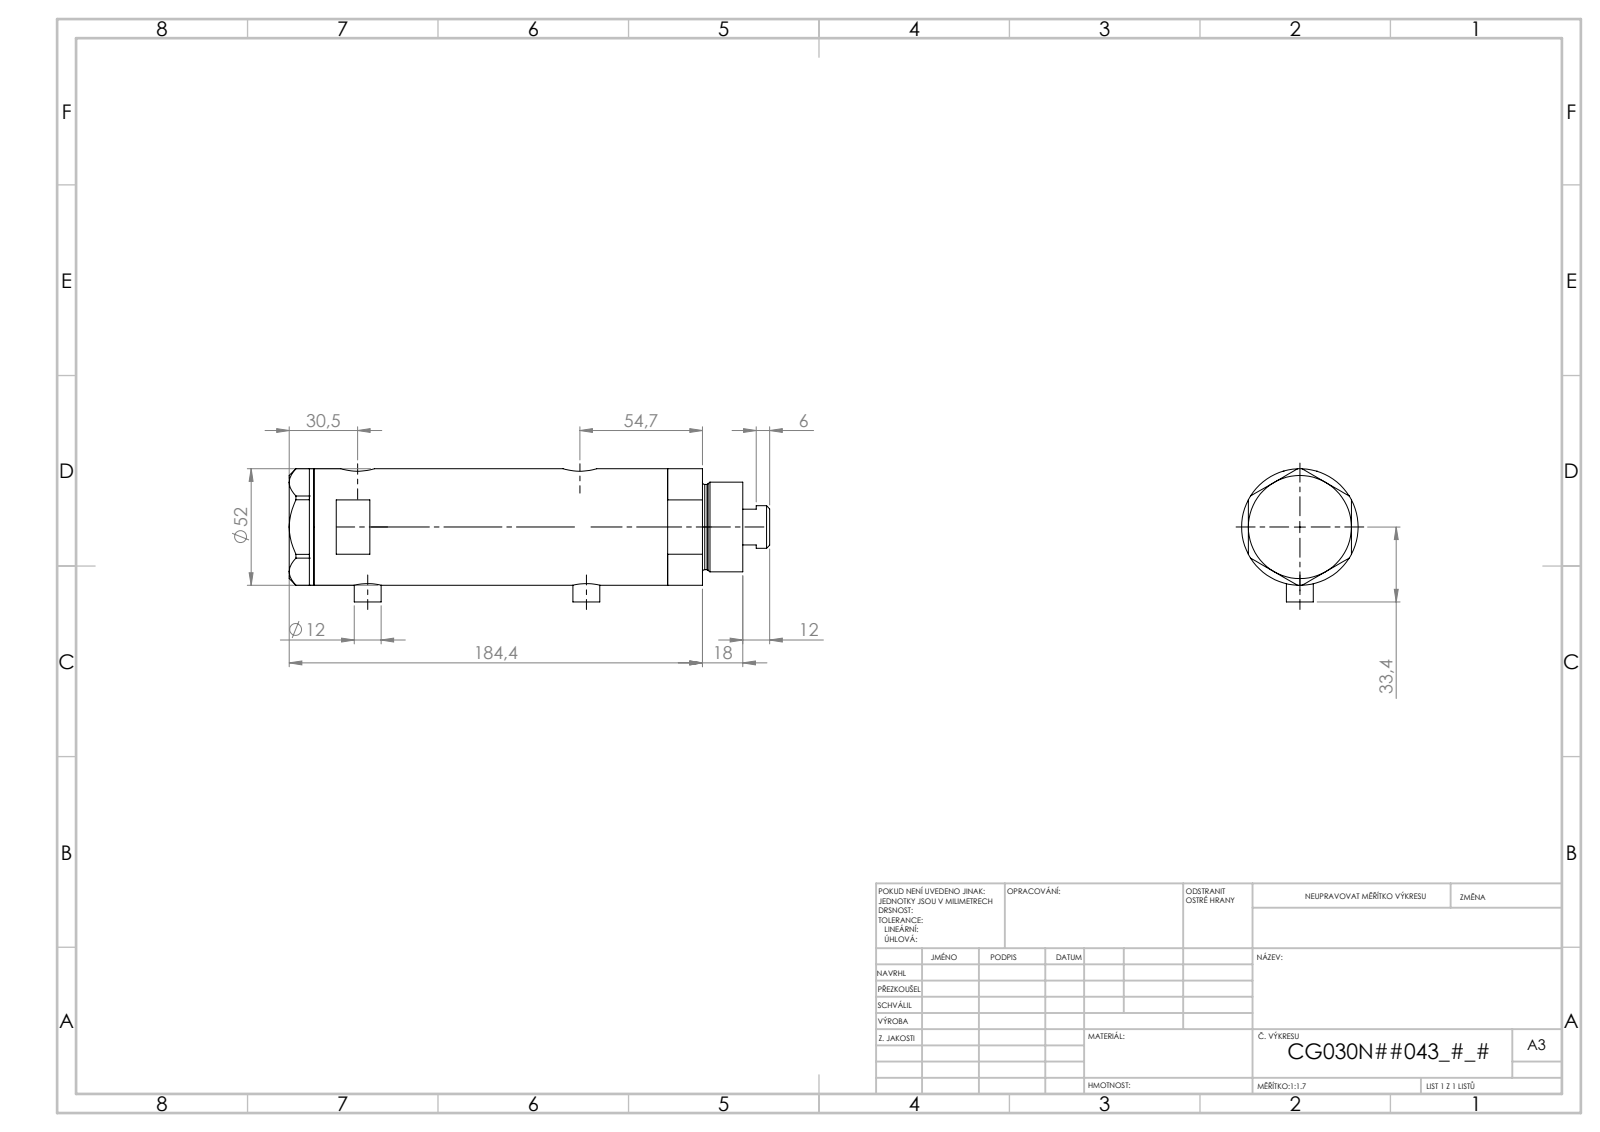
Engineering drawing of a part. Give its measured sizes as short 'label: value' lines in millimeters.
name: V270CG_VC; V270CG_FRONT; V270CG_BACK; V270CG_MIDDLE
written by: SolidWorks 2019 (CONFIG_CONTROL_DESIGN)
unit: mm
bodies: 4 solids, 140 faces (67 planar, 53 cylindrical, 20 other)
size: 192.02 × 53.1 × 52
volume: 341 952 mm³; area: 78 868 mm²
holes: 2× ⌀5, 2× ⌀9.73, 2× ⌀12.5, 2× ⌀15, 1× ⌀6.5, 1× ⌀20, 1× ⌀21.5, 1× ⌀30, 1× ⌀33, 1× ⌀44
bosses: 2× ⌀12, 1× ⌀52, 1× ⌀40, 1× ⌀38, 1× ⌀19
face distances: 96.54, 23.8, 72.74, 11, 34.8, 107.54, 46, 143.94, 132.94, 109.14
hole spacings: 2.9, 4.5, 69.75, 72.65, 74.25, 77.15, 2.89, 2.91
